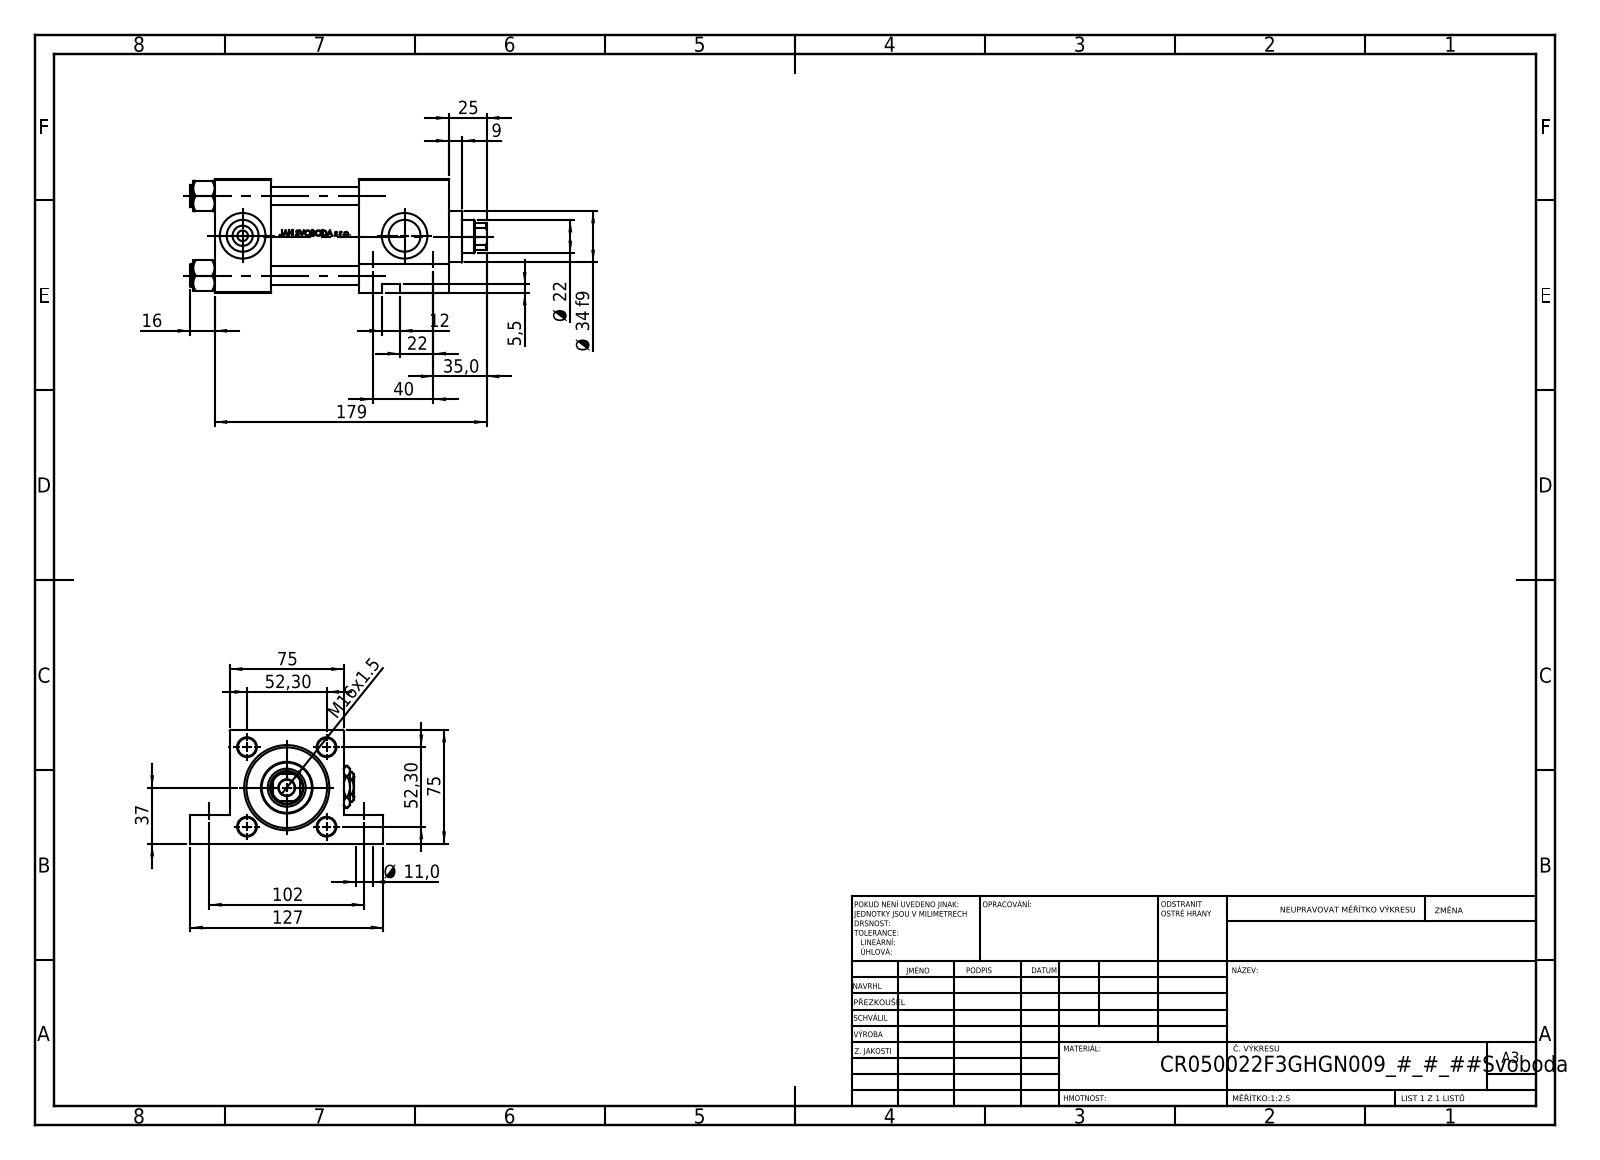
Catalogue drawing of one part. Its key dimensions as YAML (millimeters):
part_name: "V215CR_F_TYCINKA; NUT_M5_F; V215CR_F_Body; V215_VC_A (+2 more)"
step_written_by: "SolidWorks 2019 (CONFIG_CONTROL_DESIGN)"
units: millimeters
bodies: {solids: 13, faces: 1199, planar: 483, cylindrical: 134, other: 582}
overall_size: [195, 127, 75]
volume: 702130
surface_area: 160606
round_holes:
  - {diameter: 12, count: 4}
  - {diameter: 20.96, count: 3}
  - {diameter: 30, count: 3}
  - {diameter: 7, count: 2}
  - {diameter: 11, count: 2}
  - {diameter: 11, count: 2}
  - {diameter: 10.5, count: 1}
  - {diameter: 17, count: 1}
  - {diameter: 22, count: 1}
  - {diameter: 25, count: 1}
  - {diameter: 41, count: 1}
  - {diameter: 50, count: 1}
round_bosses_or_shafts:
  - {diameter: 15, count: 4}
  - {diameter: 56, count: 1}
  - {diameter: 34, count: 1}
partial_cylinders:
  - {radius: 10.5, count: 1}
face_to_face_distances: [75, 37, 154, 117, 95, 58, 59, 19, 56, 125.3]
hole_center_spacings: [52.3, 36.63, 37.34, 40, 73.96, 102, 109.56, 13]
